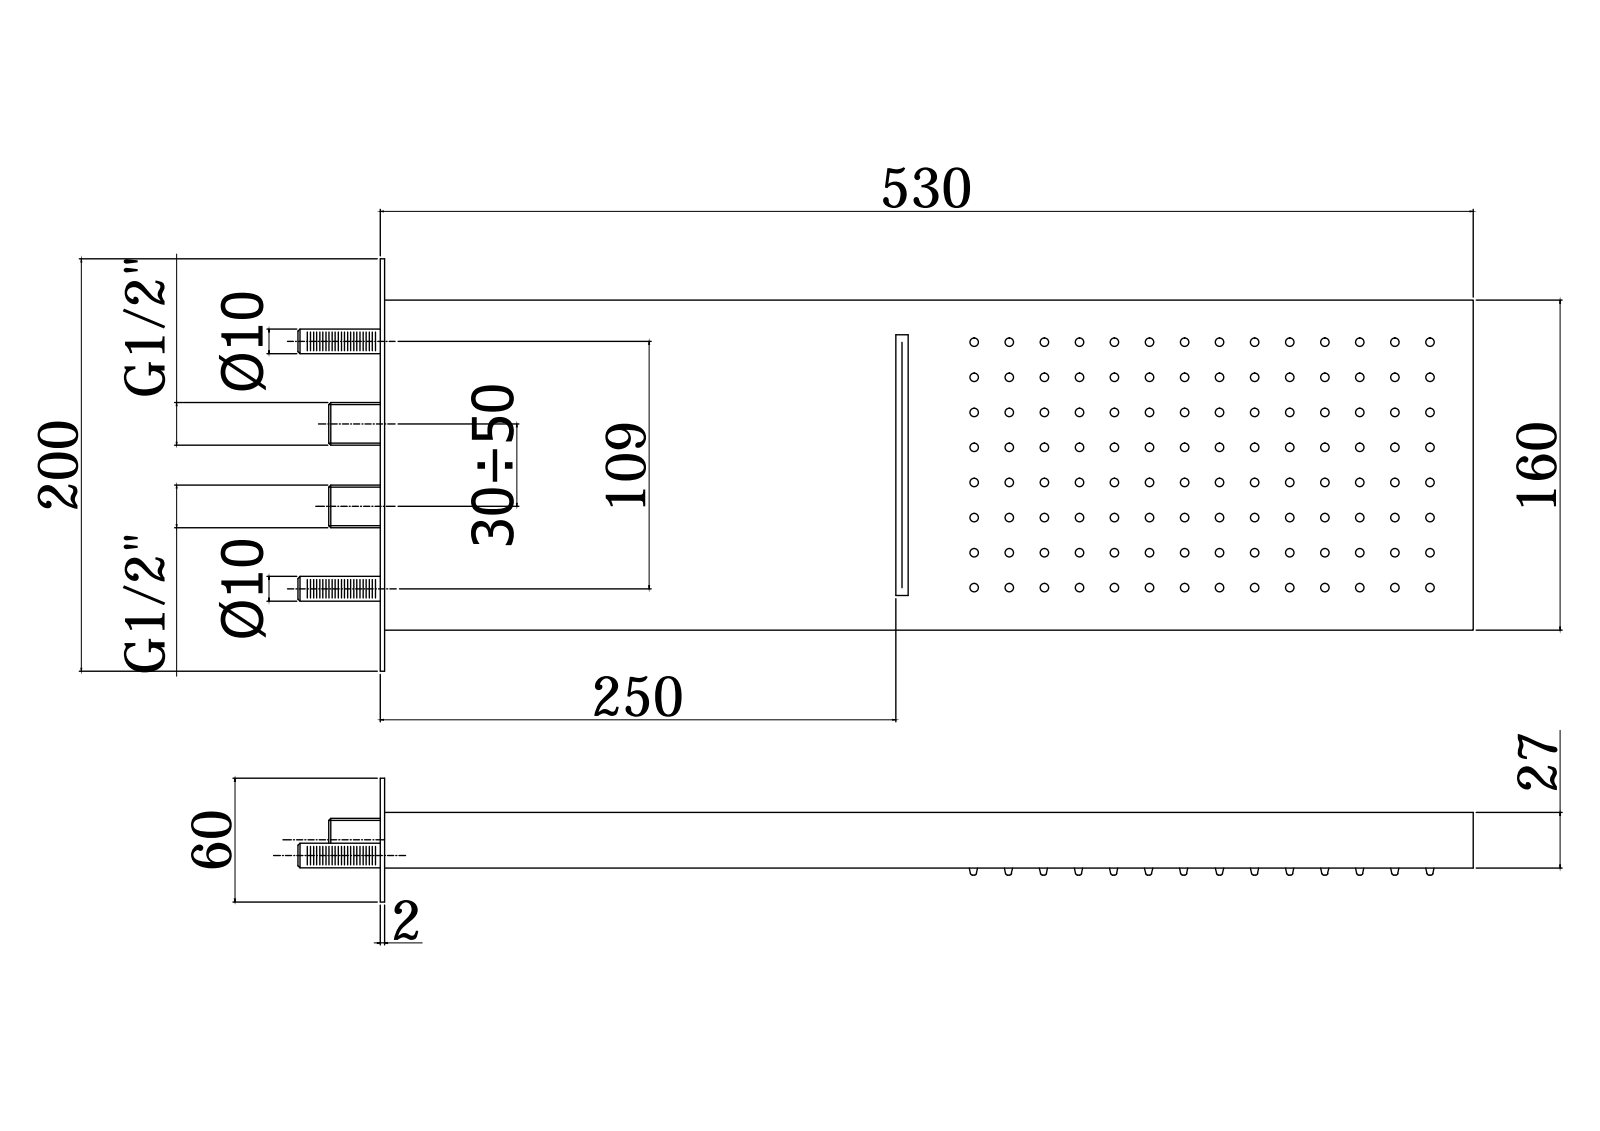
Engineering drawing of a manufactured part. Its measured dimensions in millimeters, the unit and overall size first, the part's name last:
Units: millimetres
Overall size (bounding box): 501.5 × 200 × 67
Round holes (diameter × count): ⌀3.2 ×1
Round bosses / shafts (diameter × count): ⌀25 ×2, ⌀13.2 ×2, ⌀12.1 ×2, ⌀10.9 ×2, ⌀9 ×2, ⌀7 ×2, ⌀5.6 ×2, ⌀4 ×2
Partial cylindrical surfaces — rounded edges, fillets, slot ends (radius × count): R2 ×46, R1 ×21, R1.3 ×11, R2.3 ×11, R0.5 ×7, R2.6 ×4, R4.6 ×4, R0.25 ×2
Main face-to-face distances: 1, 26, 27, 25, 3, 2, 24, 23, 21.5, 5.5
Volume: 471 339 mm³ · Surface area: 499 769 mm²
Bodies: 1 solid, 1006 faces (365 planar, 175 cylindrical, 466 other)
Part name (STEP PRODUCT): ZSOF099CR
STEP written by: CREO PARAMETRIC BY PTC INC, 2020044 (CONFIG_CONTROL_DESIGN)
